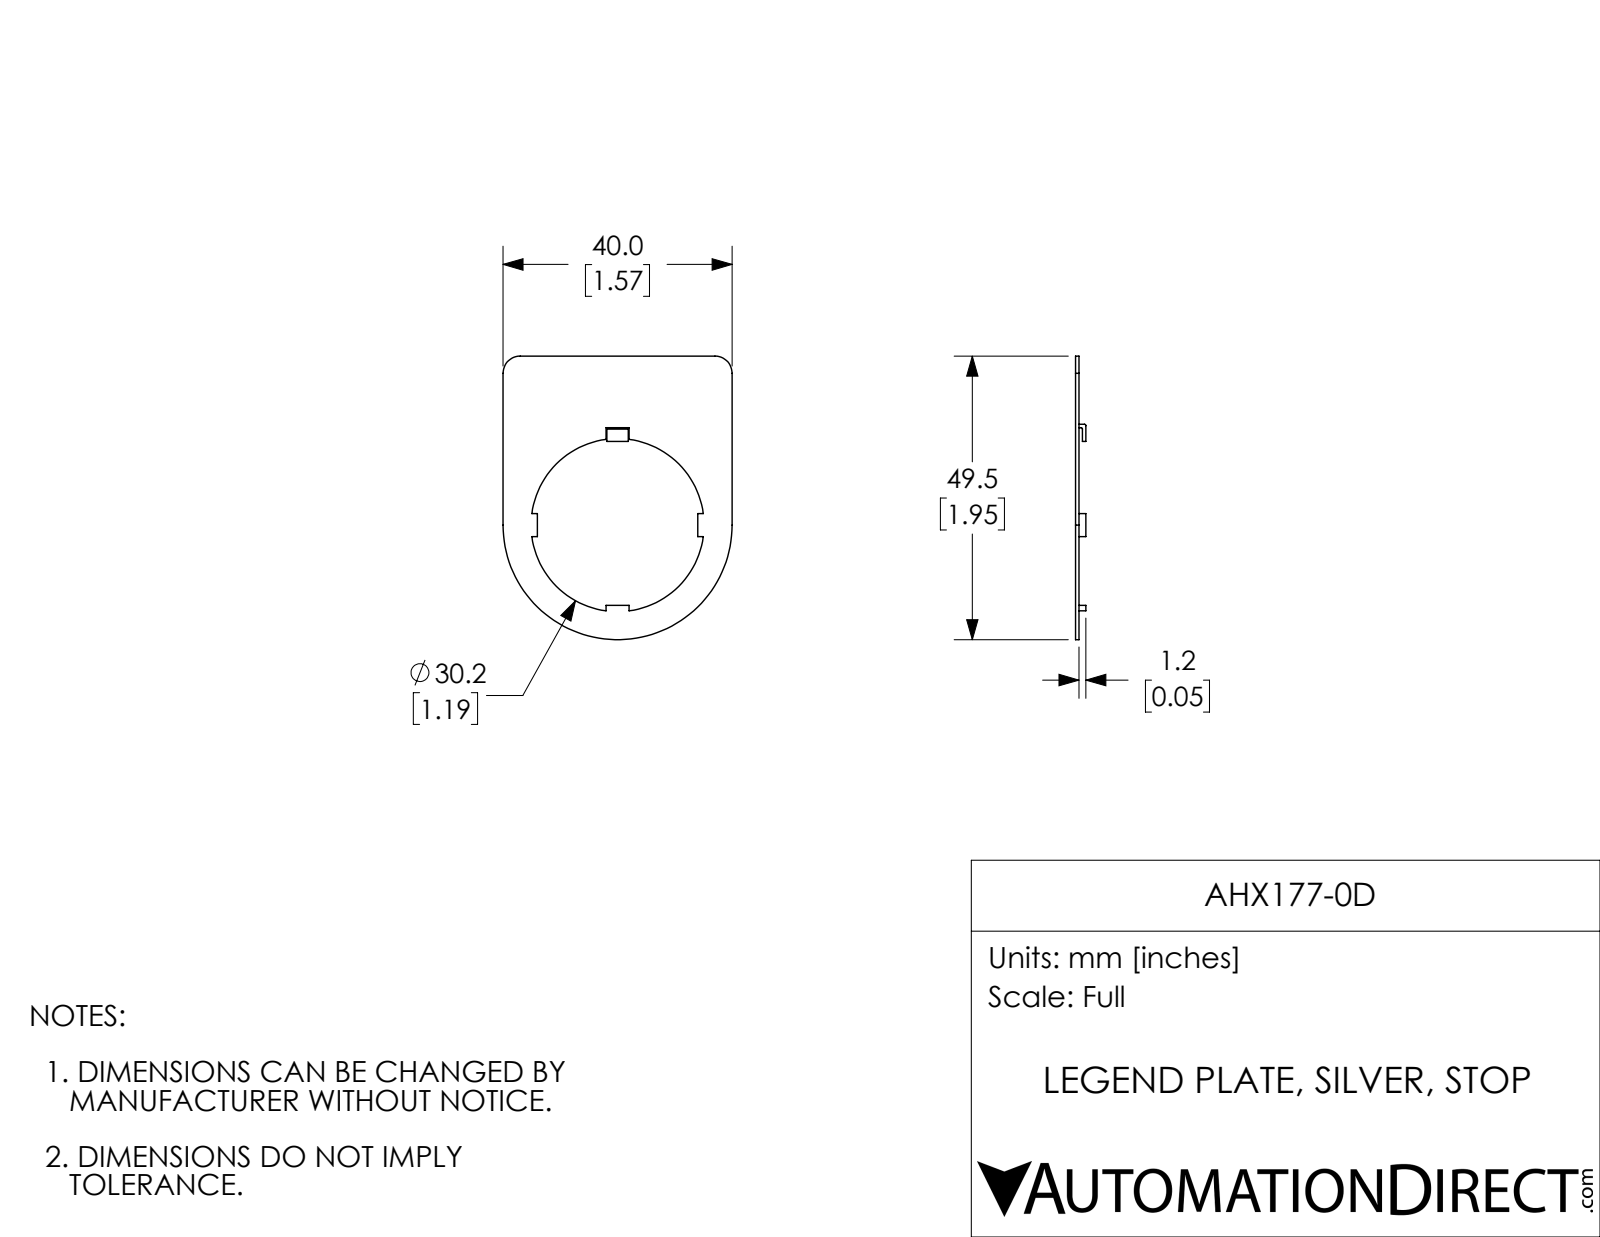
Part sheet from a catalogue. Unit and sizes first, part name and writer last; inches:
Units: inches
Overall size (bounding box): 1.949 × 1.575 × 0.071
Round holes (diameter × count): ⌀1.189 ×1
Partial cylindrical surfaces — rounded edges, fillets, slot ends (radius × count): R0.01 ×2, R0.118 ×2, R0.787 ×1
Main face-to-face distances: 0.024, 0.047, 0.071, 1.575, 0.038, 0.236, 1.339, 0.198, 1.377, 1.141
Volume: 0.041 in³ · Surface area: 3.736 in²
Bodies: 1 solid, 38 faces (29 planar, 9 cylindrical, 0 other)
Part name (STEP PRODUCT): AHX177-0D
STEP written by: SolidWorks 2017 (AUTOMOTIVE_DESIGN)
